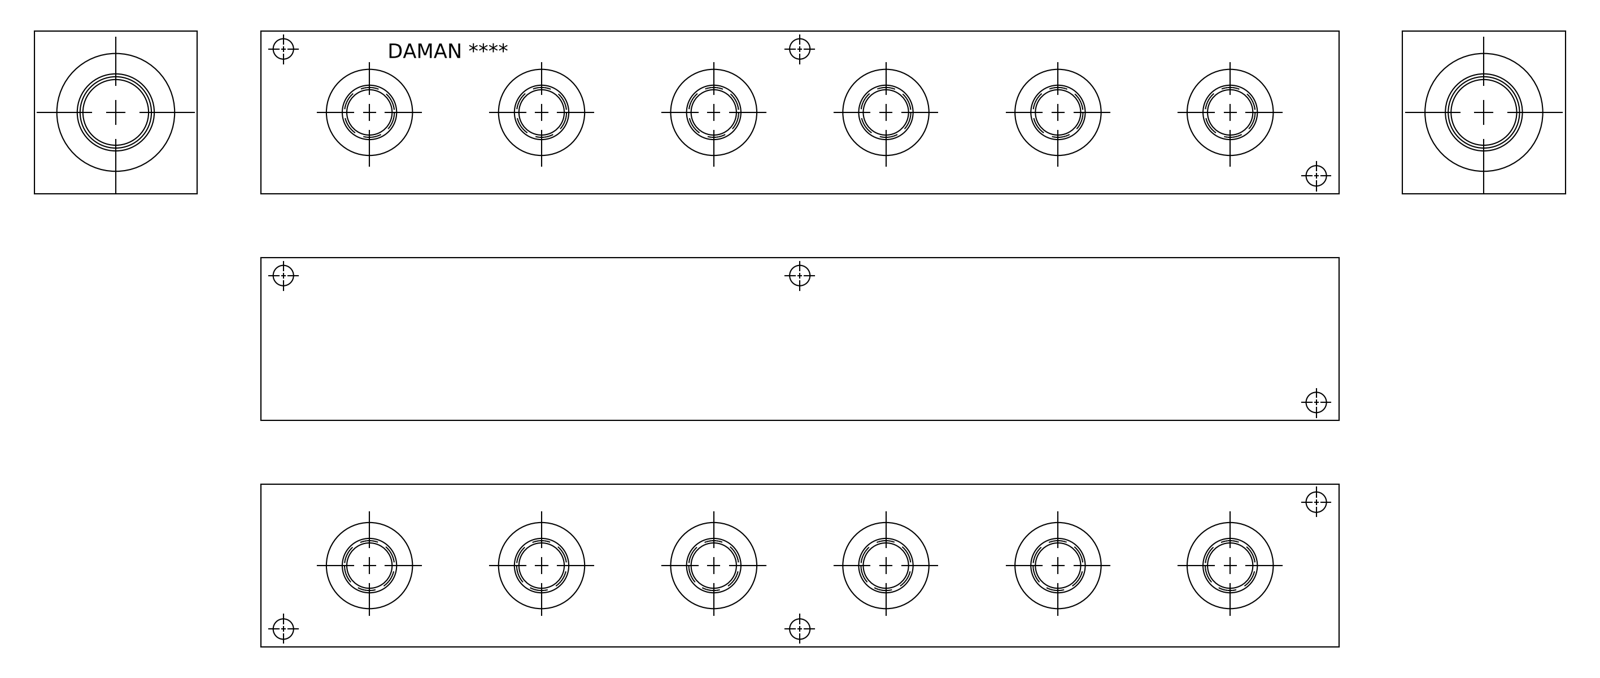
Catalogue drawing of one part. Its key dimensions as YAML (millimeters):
part_name: "Part_AH1800608S_3D"
step_written_by: "Autodesk Inventor 2019 (AUTOMOTIVE_DESIGN)"
units: millimeters
bodies: {solids: 1, faces: 485, planar: 237, cylindrical: 78, other: 170}
overall_size: [377.82, 57.15, 57.15]
volume: 1108000
surface_area: 119808
round_holes:
  - {diameter: 7.14, count: 6}
  - {diameter: 17.5, count: 6}
  - {diameter: 19.05, count: 6}
  - {diameter: 19.25, count: 6}
  - {diameter: 30.63, count: 6}
  - {diameter: 15.88, count: 4}
  - {diameter: 23.01, count: 1}
  - {diameter: 24.92, count: 1}
  - {diameter: 26.99, count: 1}
  - {diameter: 27, count: 1}
  - {diameter: 27.43, count: 1}
  - {diameter: 42.04, count: 1}
face_to_face_distances: [57.15, 0.79, 56.36, 55.57, 377.82, 377.04, 0.78, 376.25, 377.03, 41.3]
hole_center_spacings: [60.33, 120.65, 37.45, 37.48, 60.32, 93.16, 152.43, 152.46]
